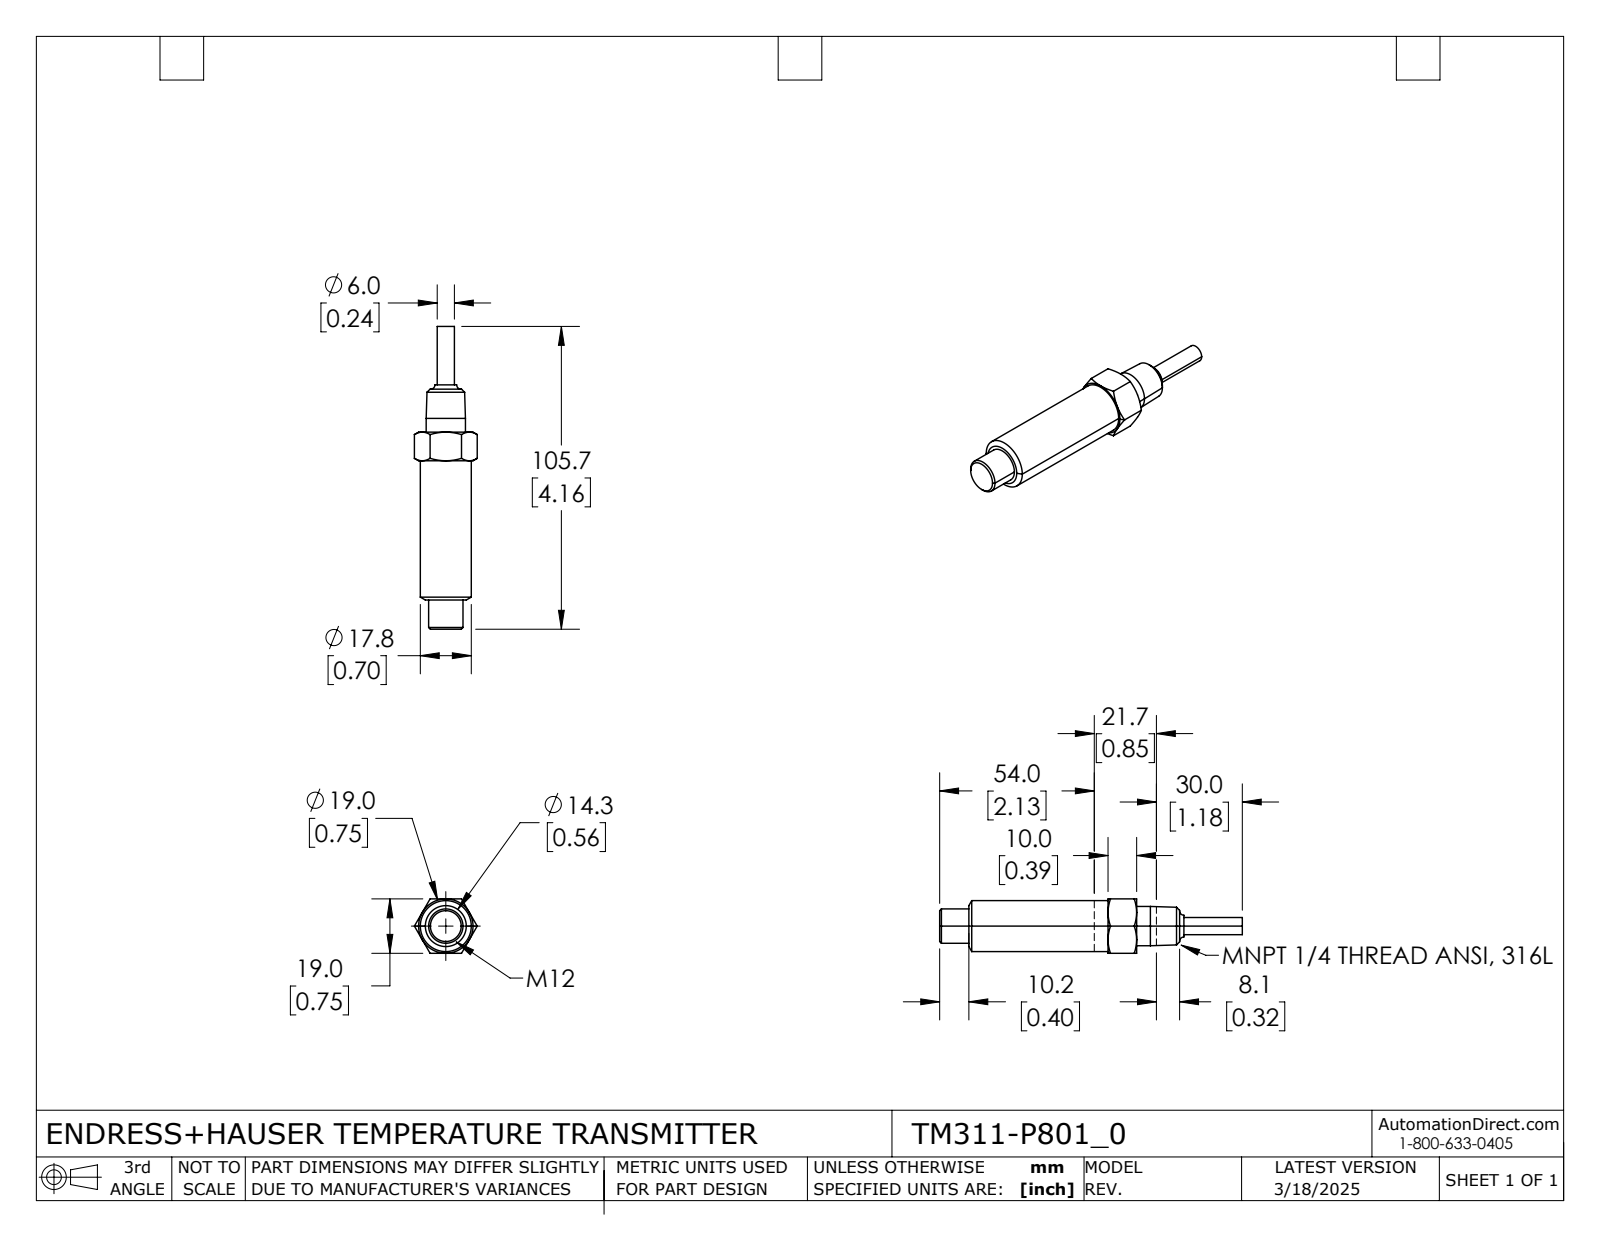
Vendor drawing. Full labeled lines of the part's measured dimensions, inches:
Part name (STEP PRODUCT): TM311-P801_0
STEP written by: SolidWorks 2021 (AUTOMOTIVE_DESIGN)
Units: inches
Bodies: 1 solid, 47 faces (13 planar, 8 cylindrical, 26 other)
Overall size (bounding box): 4.161 × 0.864 × 0.748
Volume: 1.165 in³ · Surface area: 8.219 in²
Round bosses / shafts (diameter × count): ⌀0.701 ×1, ⌀0.54 ×1, ⌀0.472 ×1, ⌀0.236 ×1
Main face-to-face distances: 0.748, 2.709, 2.307, 0.402, 0.394, 1.913, 2.315, 1.453, 1.846, 3.76
